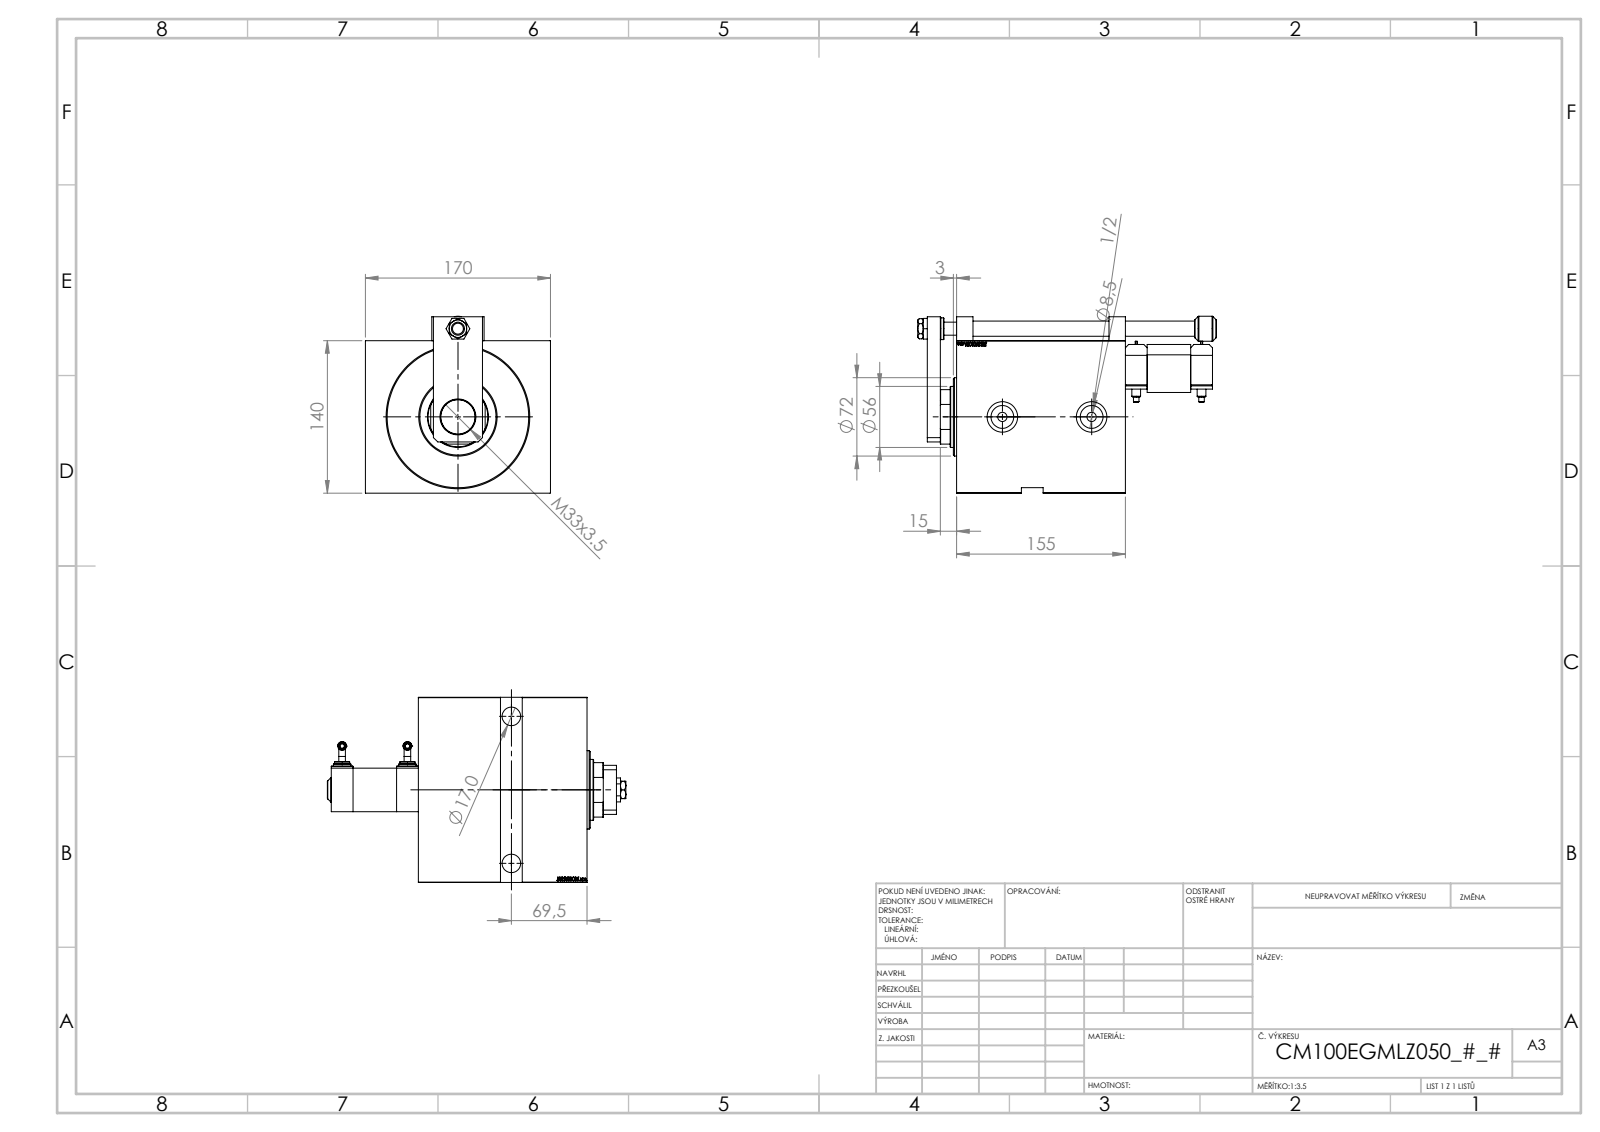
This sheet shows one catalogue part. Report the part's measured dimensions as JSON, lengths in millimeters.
{"part_name": "SWITCH P; ZARAZKA_P; TYC_P; KROUZEK_PRO_TYC (+7 more)", "step_written_by": "SolidWorks 2019 (CONFIG_CONTROL_DESIGN)", "units": "millimeters", "bodies": {"solids": 14, "faces": 1104, "planar": 527, "cylindrical": 112, "other": 465}, "overall_size": [274.3, 170, 162.5], "volume_mm3": 3354000, "surface_area_mm2": 347159, "round_holes": [[4, 4], [8, 4], [8.5, 2], [17, 2], [20.96, 2], [25, 2], [28, 2], [12, 1], [13, 1], [14, 1], [31.5, 1], [33, 1]], "round_bosses_or_shafts": [[20, 3], [16, 2], [14, 2], [8, 2], [6, 2], [5.04, 2], [72, 1], [23, 1]], "partial_cylinders_radius": [[3, 1], [22, 1]], "face_to_face_distances": [170, 140, 155, 26, 129, 5, 20, 150, 124, 15], "hole_center_spacings": [20, 84.56, 96.9, 99.25, 109.96, 140, 141.42, 81]}
